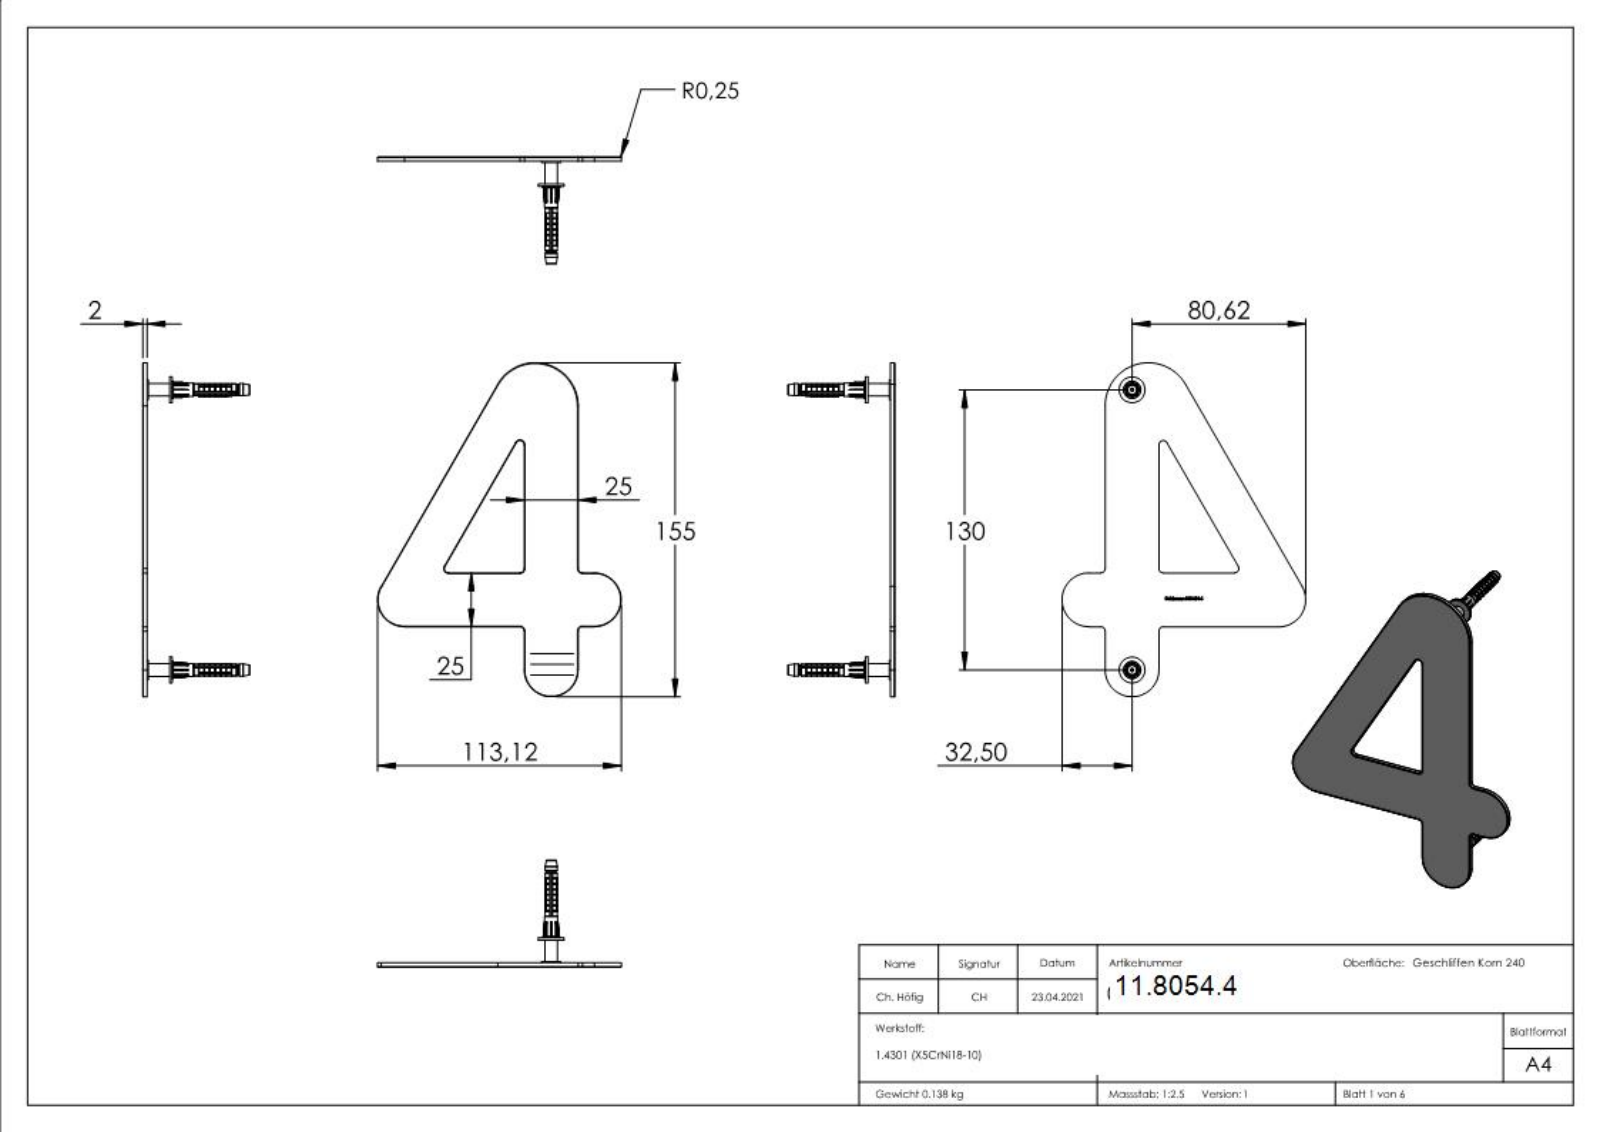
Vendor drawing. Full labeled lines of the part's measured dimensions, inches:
Part name (STEP PRODUCT): 040-HN-X Teil1; 040-HN-X Teil2_040-HN-X Teil2; 040-HN-X Teil1_040-HN-4 Teil1; 040-HN-X Teil4 (+5 more)
STEP written by: SolidWorks 2018 (CONFIG_CONTROL_DESIGN)
Units: inches
Bodies: 7 solids, 1578 faces (375 planar, 400 cylindrical, 803 other)
Overall size (bounding box): 393.701 × 205.411 × 181.413
Volume: 1.126 in³ · Surface area: 33.11 in²
Round holes (diameter × count): ⌀0.13 ×2, ⌀0.169 ×2
Round bosses / shafts (diameter × count): ⌀0.472 ×2, ⌀0.354 ×2, ⌀0.315 ×2, ⌀0.236 ×2, ⌀0.228 ×2, ⌀0.22 ×2, ⌀0.181 ×2, ⌀0.157 ×2
Partial cylindrical surfaces — rounded edges, fillets, slot ends (radius × count): R0.004 ×22, R0.01 ×6, R0.079 ×6, R0.492 ×3, R0.138 ×2, R0.787 ×1
Main face-to-face distances: 0.079, 0.457, 0.535, 0.492, 0.043, 0.413, 0.984, 0.827, 0.02, 0.098
Hole centre spacings: 5.118
